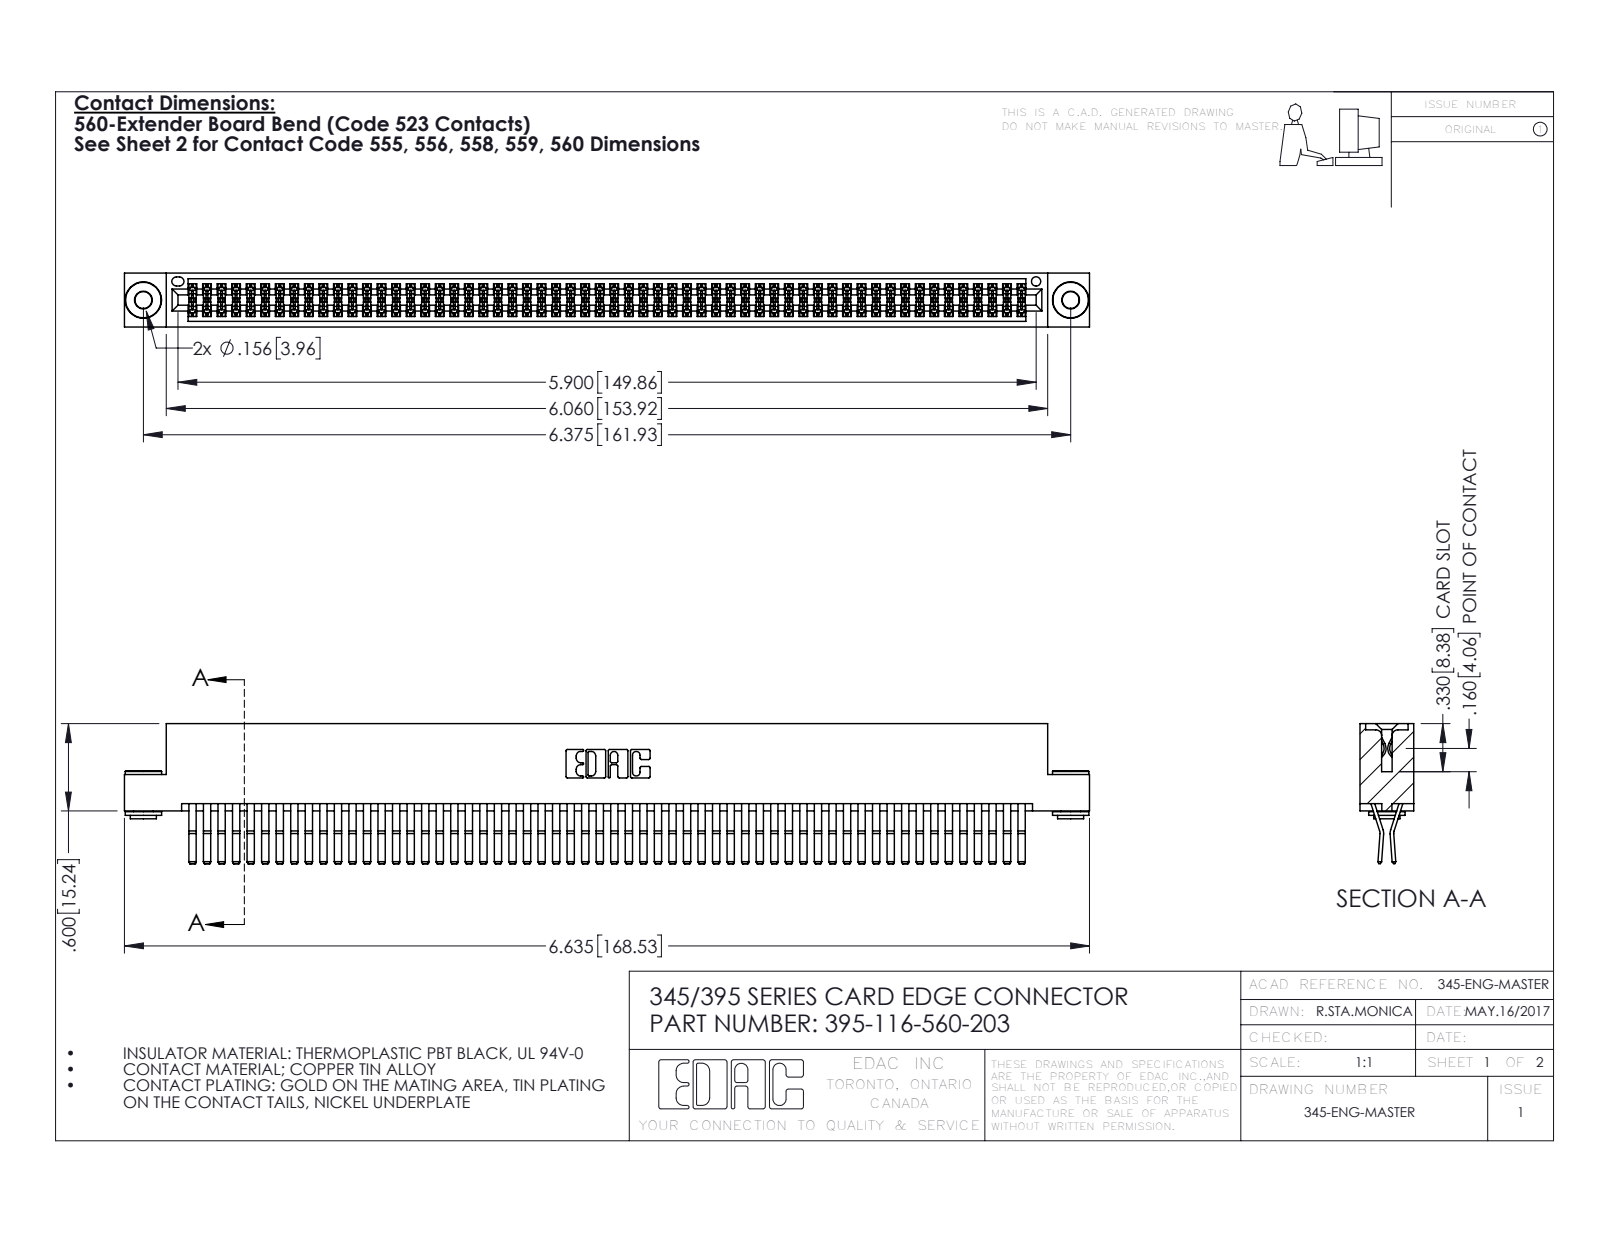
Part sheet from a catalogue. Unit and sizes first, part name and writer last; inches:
Units: inches
Overall size (bounding box): 6.635 × 0.962 × 0.37
Round holes (diameter × count): ⌀0.116 ×2, ⌀0.156 ×2, ⌀0.064 ×1
Round bosses / shafts (diameter × count): ⌀0.25 ×2, ⌀0.18 ×2, ⌀0.136 ×2
Partial cylindrical surfaces — rounded edges, fillets, slot ends (radius × count): R0.006 ×175, R0.01 ×22, R0.007 ×6, R0.031 ×6, R0.026 ×3, R0.01 ×2, R0.014 ×2, R0.019 ×2
Main face-to-face distances: 0.025, 0.072, 0.298, 0.2, 0.37, 0.098, 0.272, 0.225, 0.175, 0.149
Hole centre spacings: 0.27, 6.139, 6.375
Volume: 1.056 in³ · Surface area: 43.46 in²
Bodies: 119 solids, 6196 faces (3918 planar, 2270 cylindrical, 8 other)
Part name (STEP PRODUCT): 345-250-002_345-250-002-102; 345-292-001_560 Tail; 345 Part_Flush Mounting Lugs - 0.156 Dia-TH; 395-116-560-203
STEP written by: SolidWorks 2016 (CONFIG_CONTROL_DESIGN)
